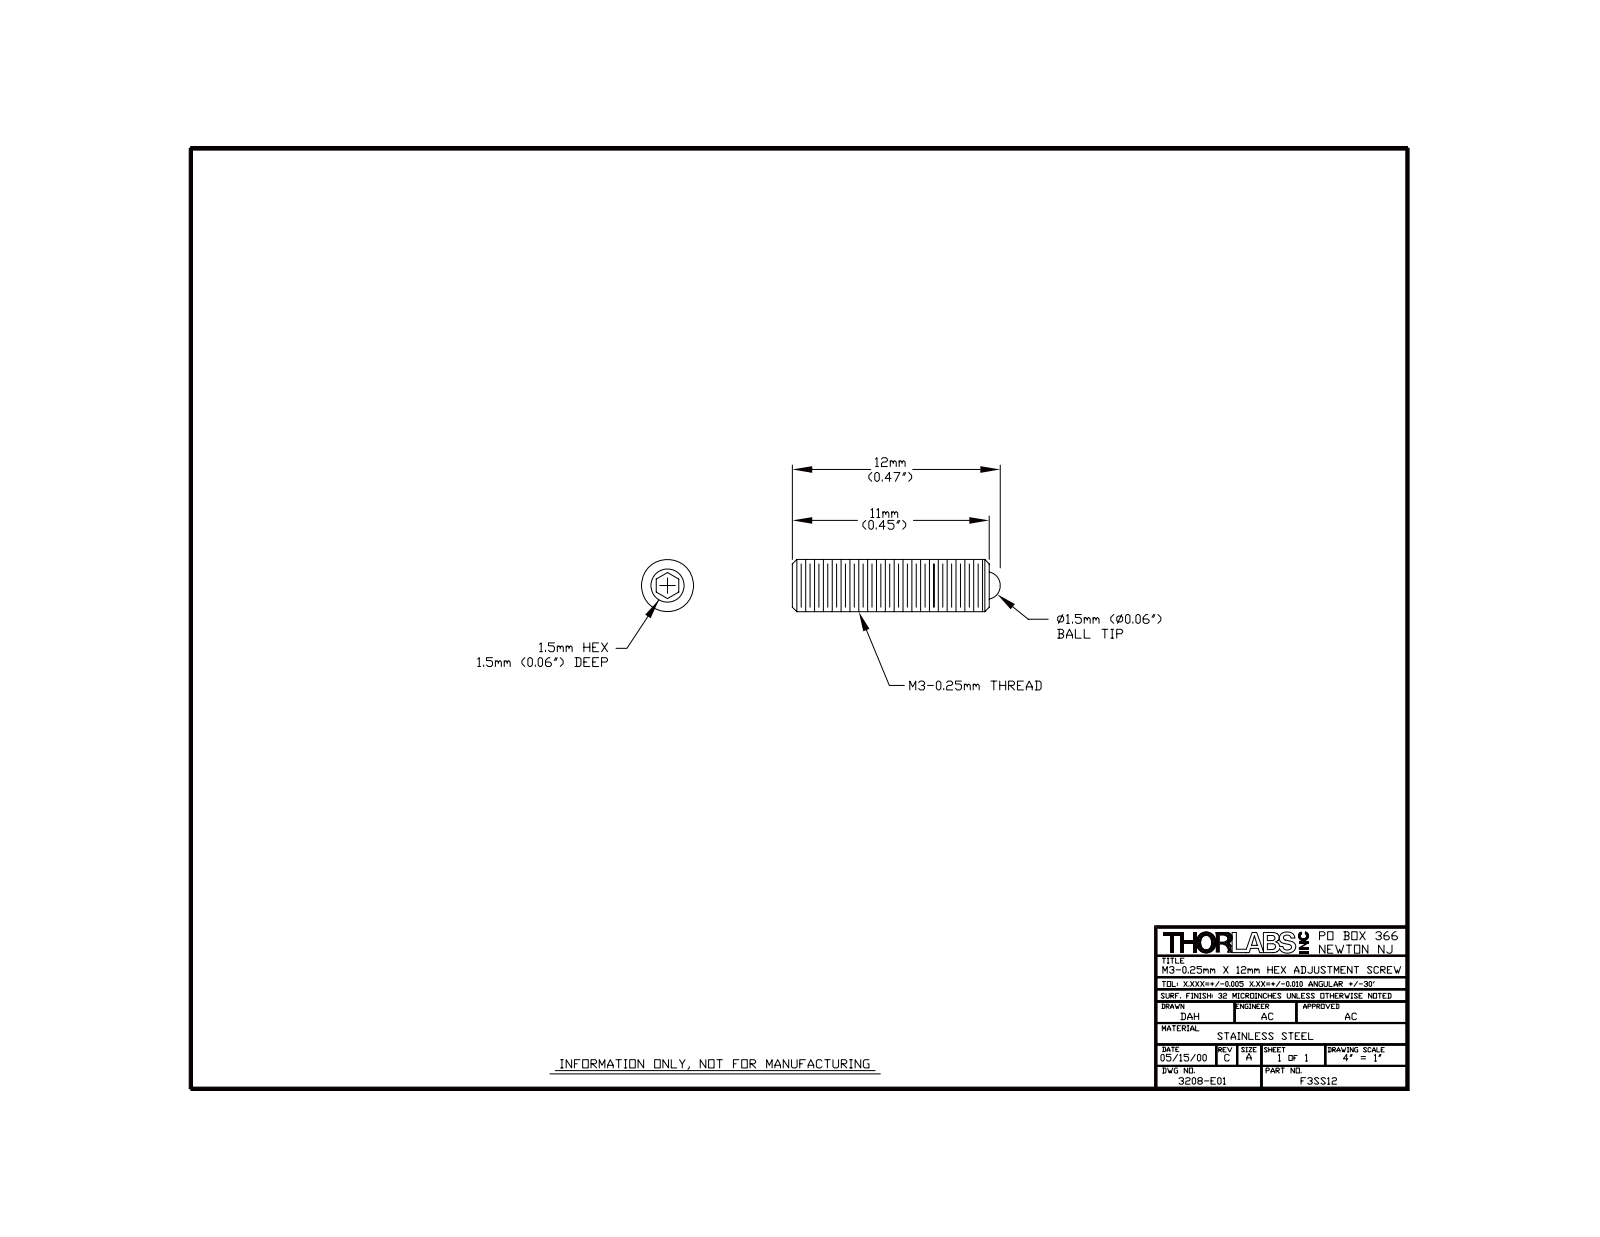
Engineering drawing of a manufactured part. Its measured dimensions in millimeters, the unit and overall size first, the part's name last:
Units: millimetres
Overall size (bounding box): 11.9 × 2.9 × 2.9
Round holes (diameter × count): ⌀1.6 ×1
Round bosses / shafts (diameter × count): ⌀2.9 ×1
Main face-to-face distances: 1.3, 11.3, 1.5, 9.8, 1.3
Volume: 80 mm³ · Surface area: 132 mm²
Bodies: 2 solids, 23 faces (9 planar, 4 cylindrical, 10 other)
Part name (STEP PRODUCT): 3208-E0W
STEP written by: SolidWorks 2011 (AUTOMOTIVE_DESIGN)
